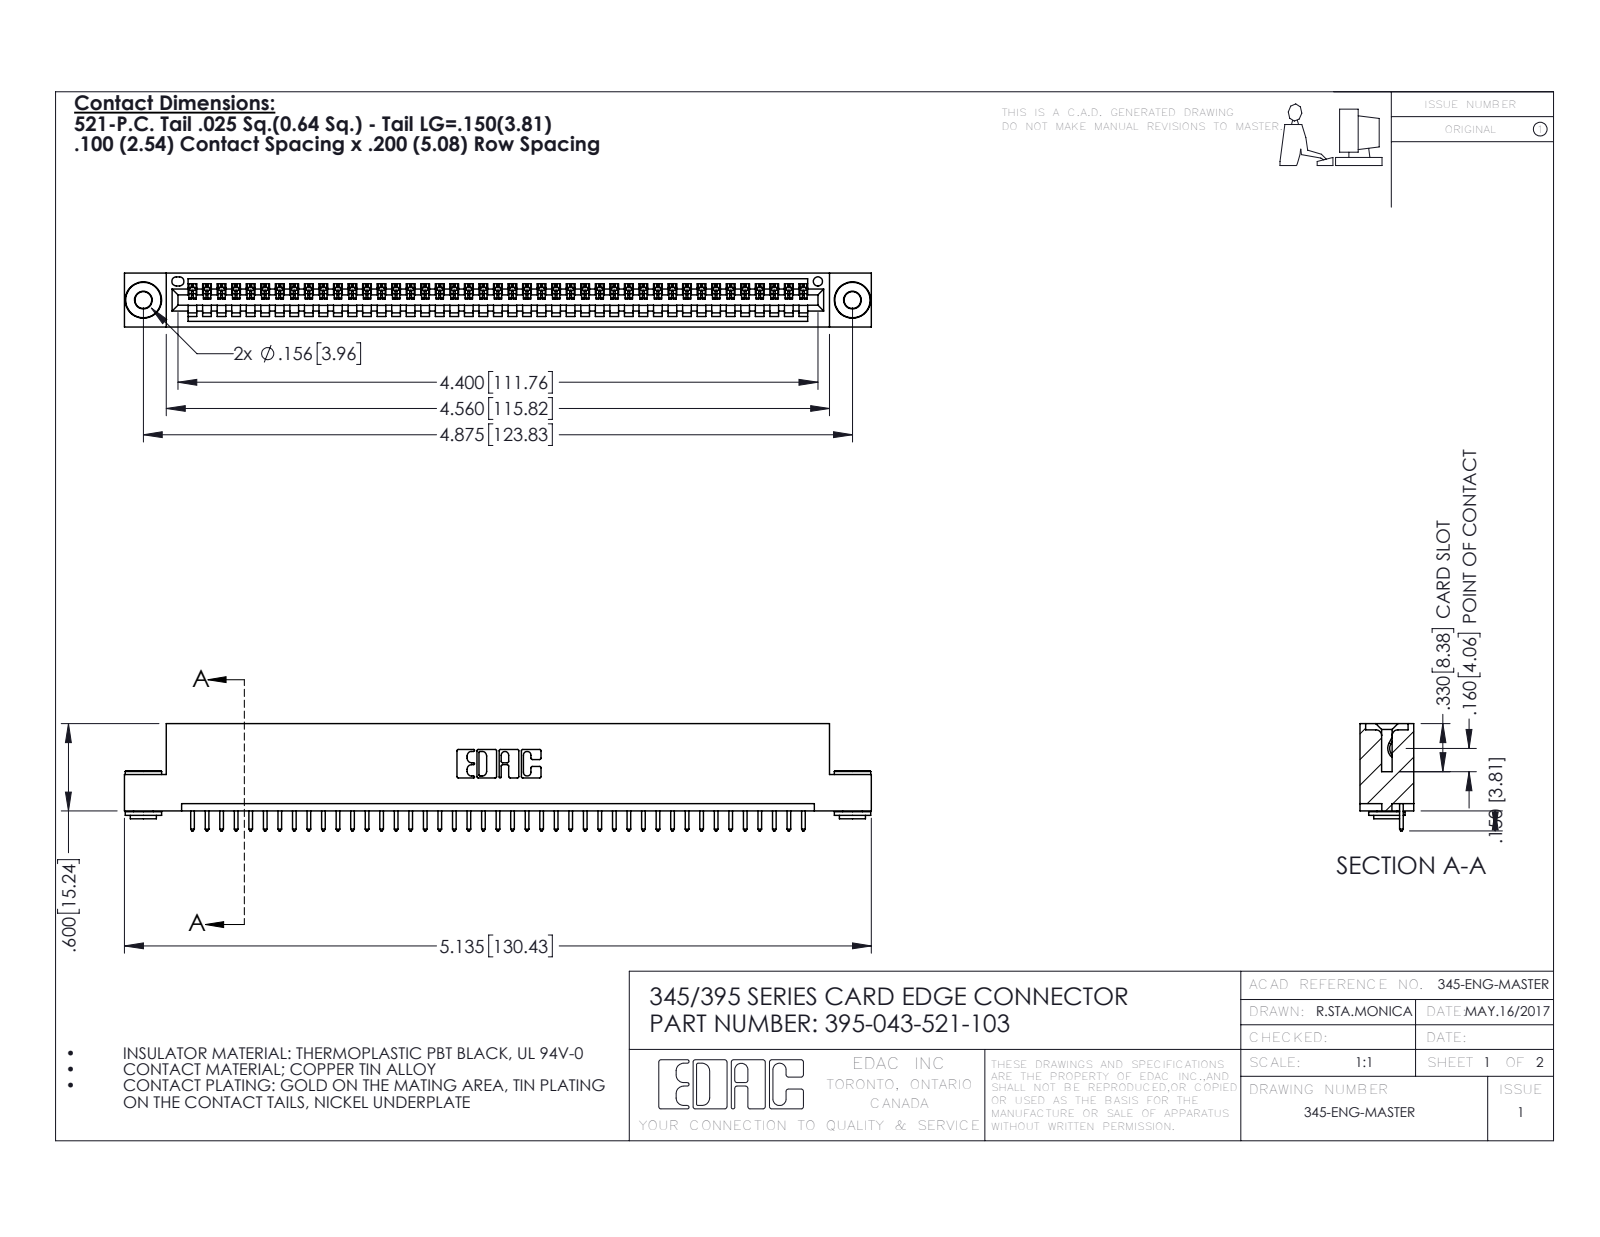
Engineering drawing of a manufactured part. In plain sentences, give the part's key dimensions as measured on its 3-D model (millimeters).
The part is named "345-250-002_345-250-002-102; 345 Part_Flush Mounting Lugs - 0.156 Dia-TH; 345-292-001_345-293-121; 395-043-521-103". Its 3-D file was written by "SolidWorks 2016 (CONFIG_CONTROL_DESIGN)". It is 46 solids with 2658 faces: 1810 planar, 840 cylindrical and 8 other. Overall it measures 130.4 by 18.7 by 9.4 millimeters. Its volume is 12 300 cubic millimeters and its surface area 16 080 square millimeters. Round holes: 2 of diameter 2.9, 2 of diameter 4, 1 of diameter 1.6. Round bosses or shafts: 2 of diameter 6.4, 2 of diameter 4.6, 2 of diameter 3.5. Partial cylindrical surfaces (rounded edges, fillets, slot ends): 86 of radius 0.2, 86 of radius 0.3, 22 of radius 0.3, 6 of radius 0.2, 6 of radius 0.8, 3 of radius 0.7, 2 of radius 0.8, 2 of radius 1. The main face-to-face distances are 1.8, 7.6, 9.4, 5.1, 0.6, 2.5, 6.9, 5.7, 3.8, 1.8. The hole center spacings are 6.9, 117.8, 123.8.
